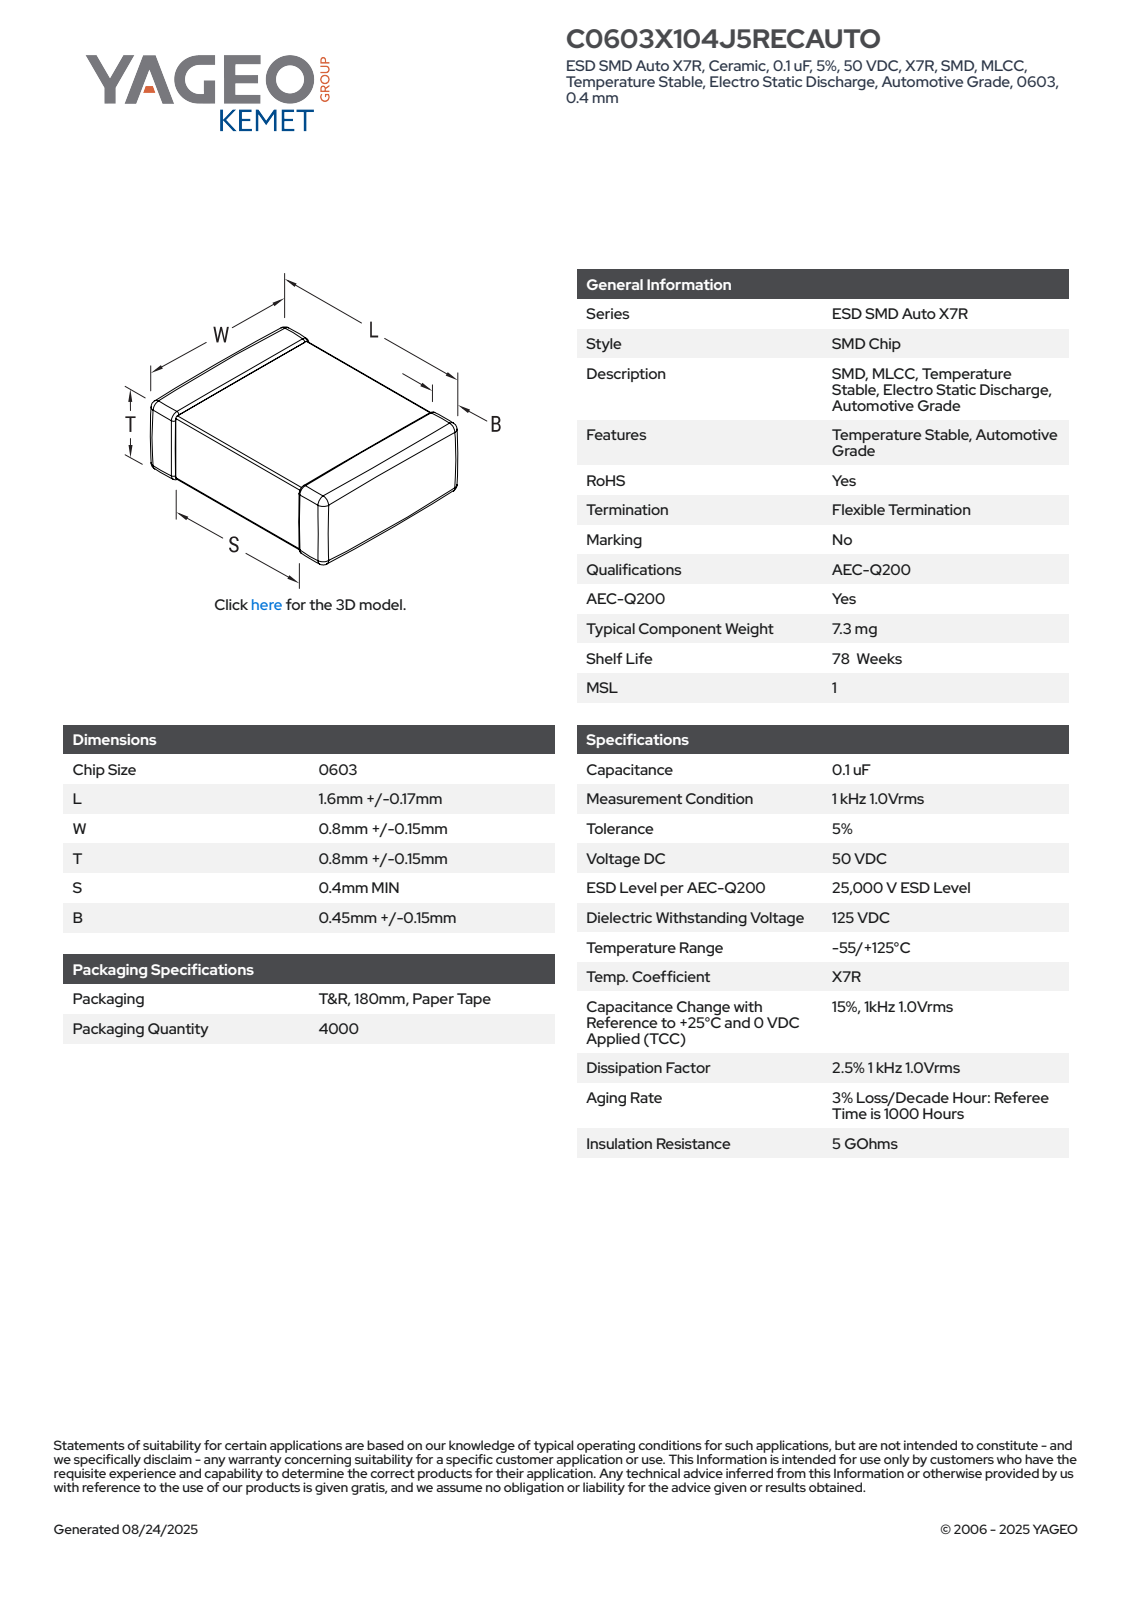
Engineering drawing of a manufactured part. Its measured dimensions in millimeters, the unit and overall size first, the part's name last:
Units: millimetres
Overall size (bounding box): 1.77 × 0.95 × 0.95
Main face-to-face distances: 0.93, 0.95, 0.91, 1.77, 0.94, 0.92, 0.82, 0.96, 0.81, 0.84
Volume: 2 mm³ · Surface area: 9 mm²
Bodies: 4 solids, 125 faces (71 planar, 38 cylindrical, 16 other)
Part name (STEP PRODUCT): CCS_CCSTD_0603_L1.77W0.95T0.95B0.45
STEP written by: SolidWorks 2021 (AUTOMOTIVE_DESIGN)
